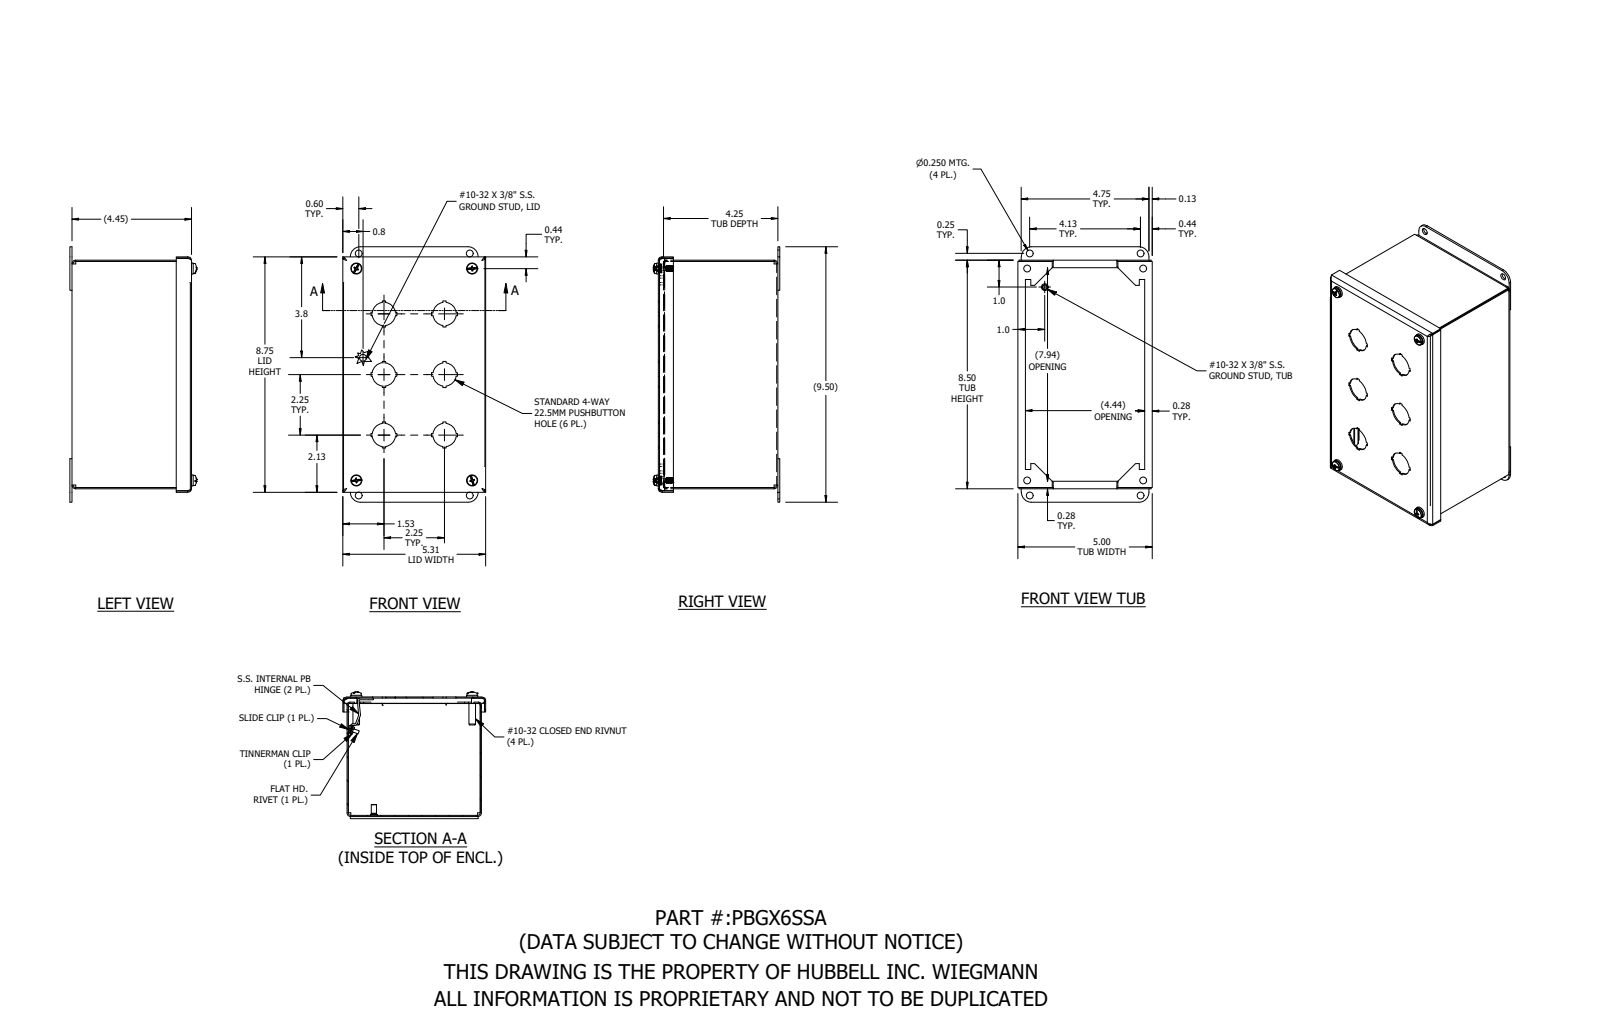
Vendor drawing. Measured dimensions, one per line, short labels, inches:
name: PBGX6SSA
written by: SolidWorks 2021 (AUTOMOTIVE_DESIGN)
unit: in
bodies: 25 solids, 928 faces (463 planar, 313 cylindrical, 152 other)
size: 9.5 × 5.313 × 4.704
volume: 14.12 in³; area: 529.9 in²
holes: 6× ⌀0.875, 4× ⌀0.156, 4× ⌀0.196, 4× ⌀0.25, 4× ⌀0.257, 4× ⌀0.281, 4× ⌀0.313, 2× ⌀0.133, 2× ⌀0.14, 2× ⌀0.175, 2× ⌀0.175
bosses: 4× ⌀0.406, 4× ⌀0.318, 4× ⌀0.248, 4× ⌀0.186, 4× ⌀0.141, 4× ⌀0.14, 3× ⌀0.375, 3× ⌀0.25
rounds: 8× R0.094, 8× R0.139, 6× R0.188, 4× R0.063, 4× R0.09, 4× R0.108, 4× R0.375, 3× R0.031
face distances: 0.045, 4.4, 0.045, 8.455, 4.445, 4.355, 4.91, 4.955, 4.955, 5
hole spacings: 2.25, 0.019, 1.978, 3.182, 3.69, 4.07, 5.125, 6.273
